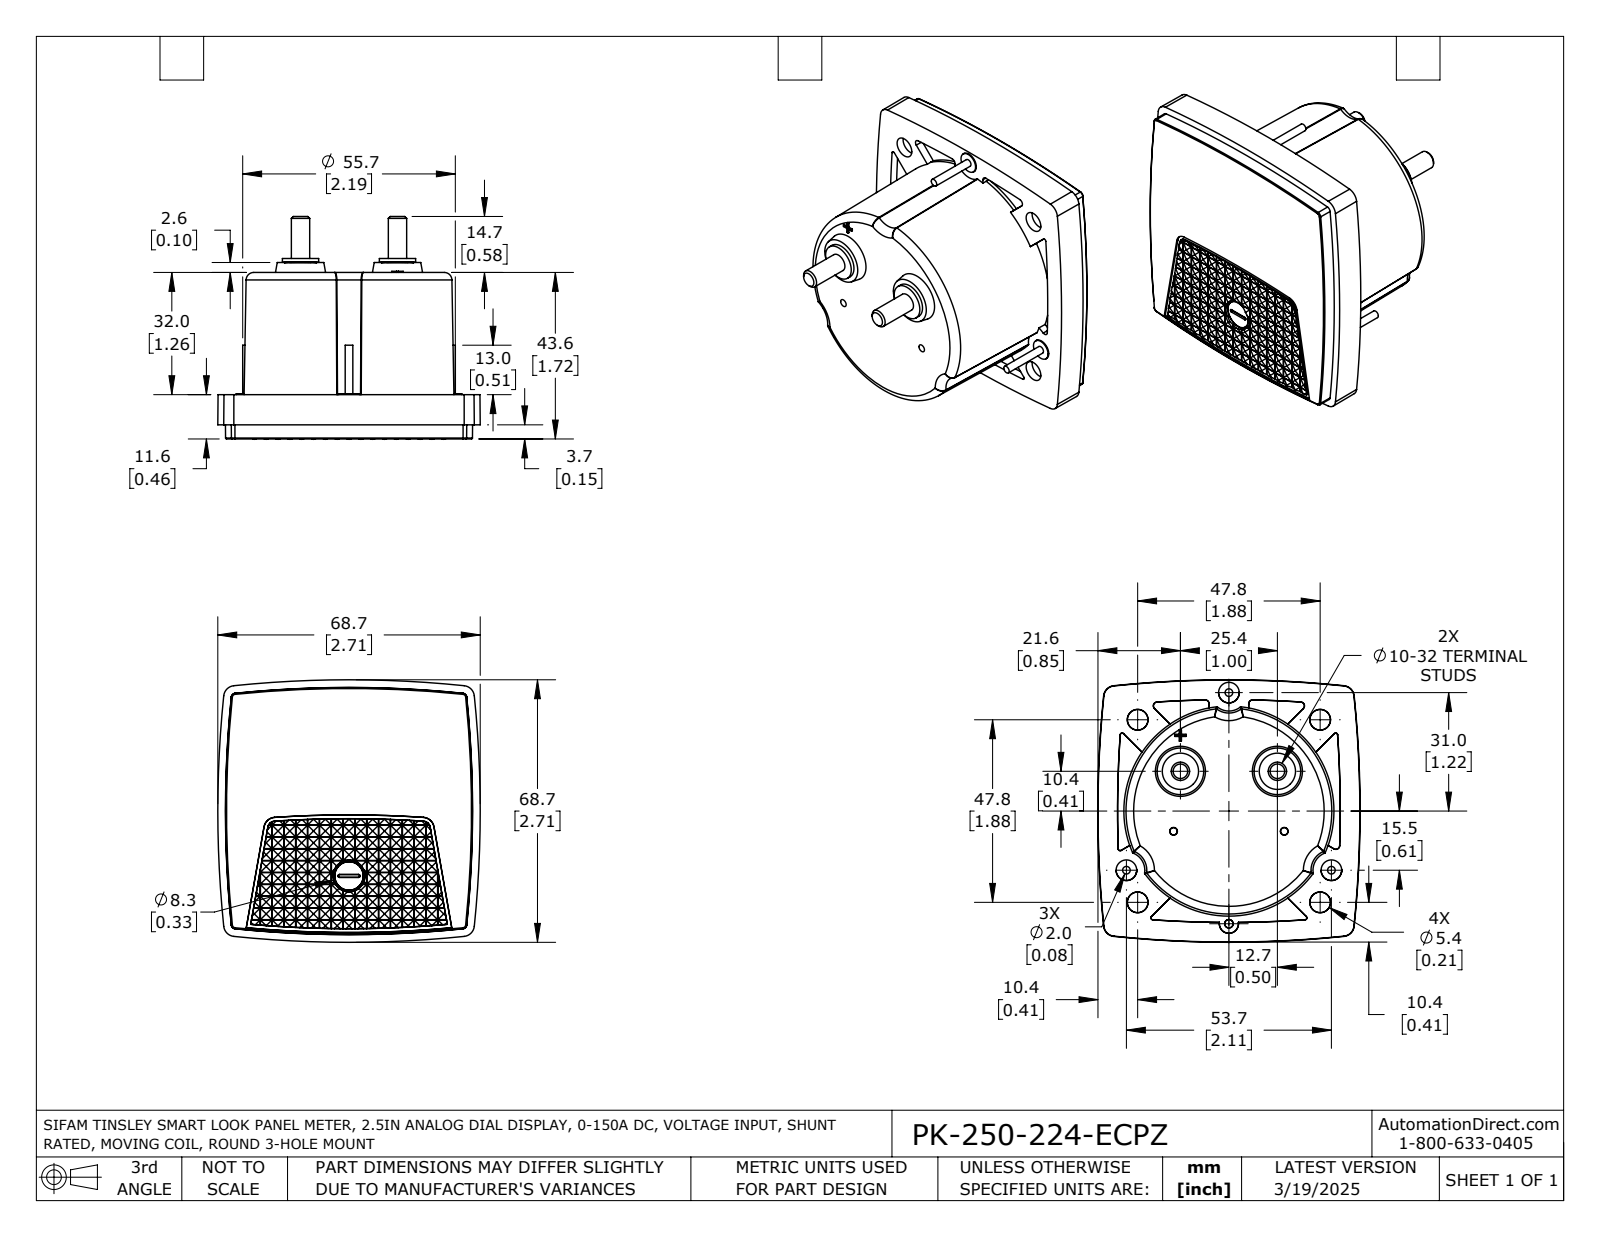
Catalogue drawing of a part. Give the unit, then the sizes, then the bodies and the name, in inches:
Units: inches
Overall size (bounding box): 2.706 × 2.706 × 2.297
Round bosses / shafts (diameter × count): ⌀0.213 ×3, ⌀0.079 ×3, ⌀0.374 ×2, ⌀0.189 ×2, ⌀0.215 ×1
Partial cylindrical surfaces — rounded edges, fillets, slot ends (radius × count): R0.167 ×2, R1.083 ×1
Main face-to-face distances: 1.717, 1.26, 0.457, 0.024, 0.087, 0.096, 0.311, 0.12, 0.072, 1.346
Volume: 7.594 in³ · Surface area: 30.41 in²
Bodies: 1 solid, 1550 faces (1165 planar, 265 cylindrical, 120 other)
Part name (STEP PRODUCT): PK-250-224-ECPZ
STEP written by: SolidWorks 2021 (AUTOMOTIVE_DESIGN)
